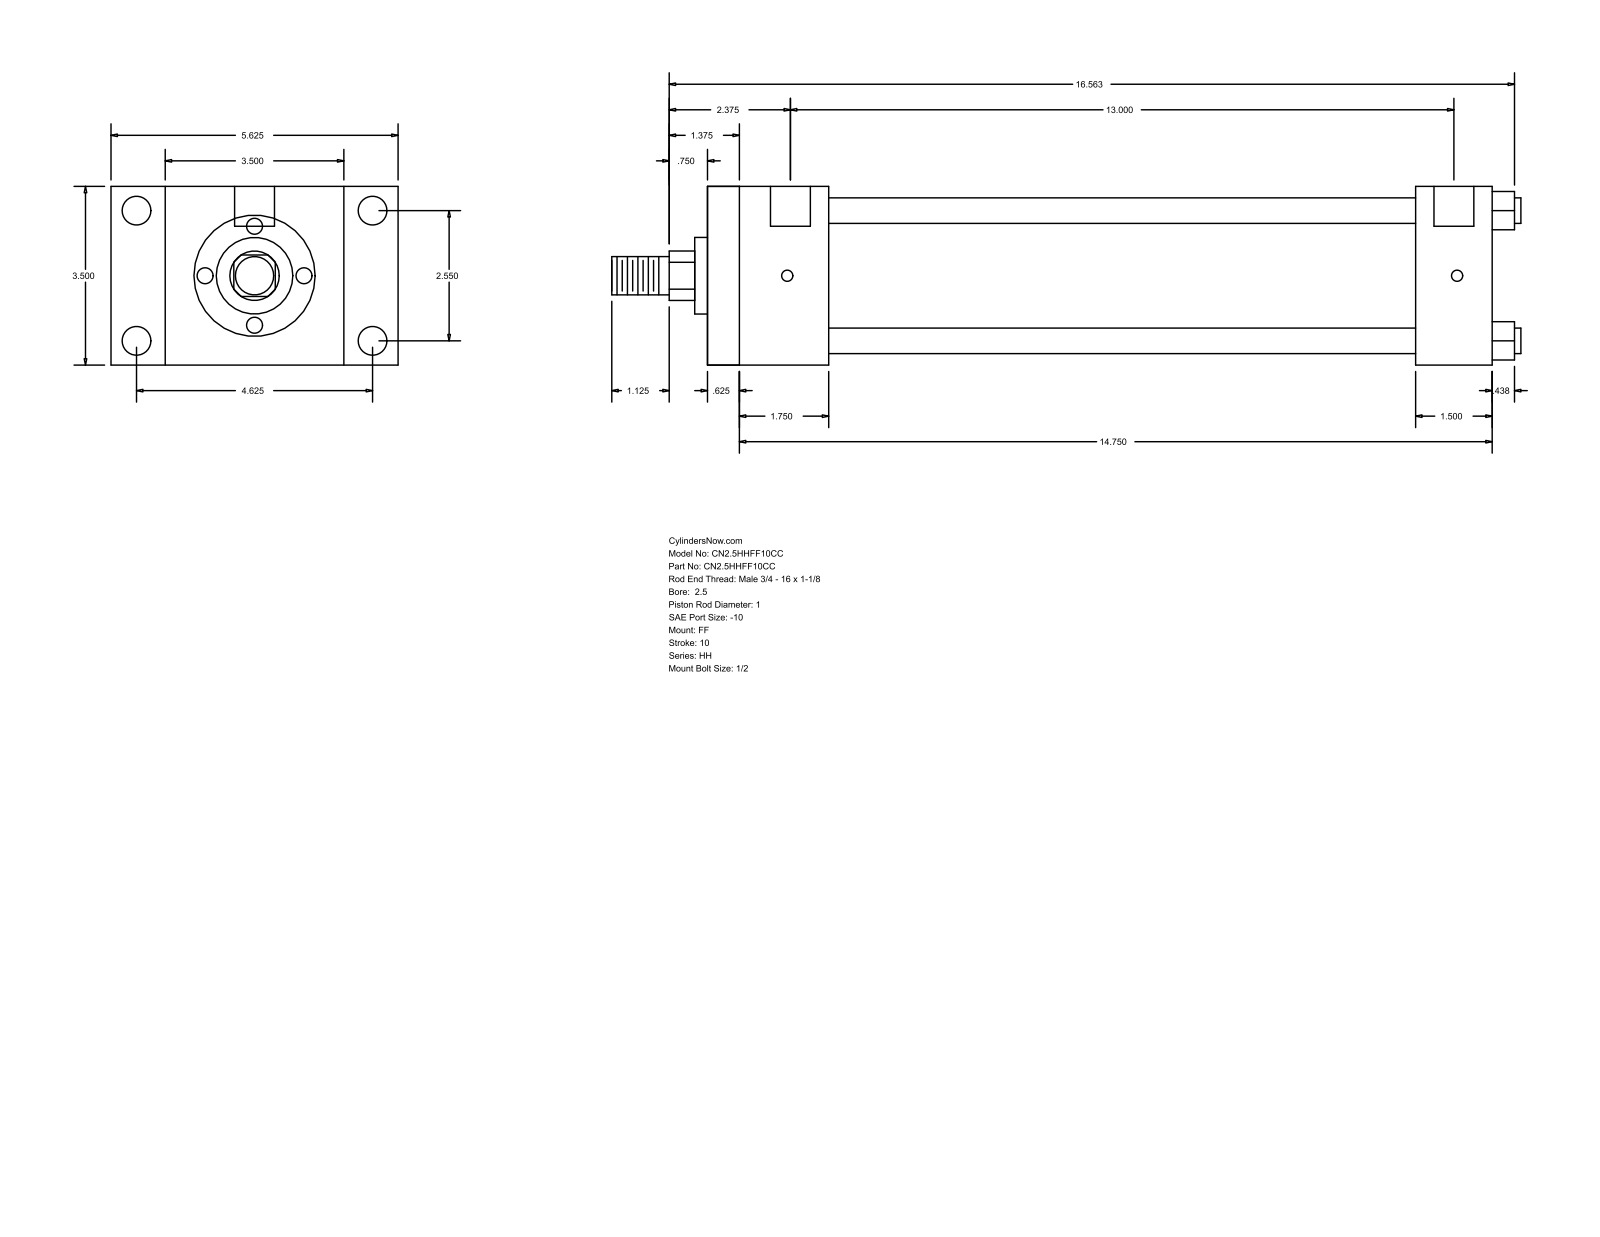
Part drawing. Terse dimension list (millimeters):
name: HH_FF__0250_1
written by: GSSL Pune (CONFIG_CONTROL_DESIGN)
unit: mm
bodies: 0 solids, 92 faces (64 planar, 28 cylindrical, 0 other)
size: 452.44 × 142.88 × 88.9
holes: 4× ⌀5.56, 4× ⌀14.3, 2× ⌀19.84
bosses: 4× ⌀12.7, 1× ⌀73.03, 1× ⌀38.1, 1× ⌀25.4, 1× ⌀19.05
rounds: 1× R12.29
face distances: 88.9, 390.52, 15.87, 374.65, 60.33, 44.46, 330.19, 352.43, 336.56, 292.1
hole spacings: 1.59, 64.76, 117.48, 134.15, 331.78, 333.37, 330.19
